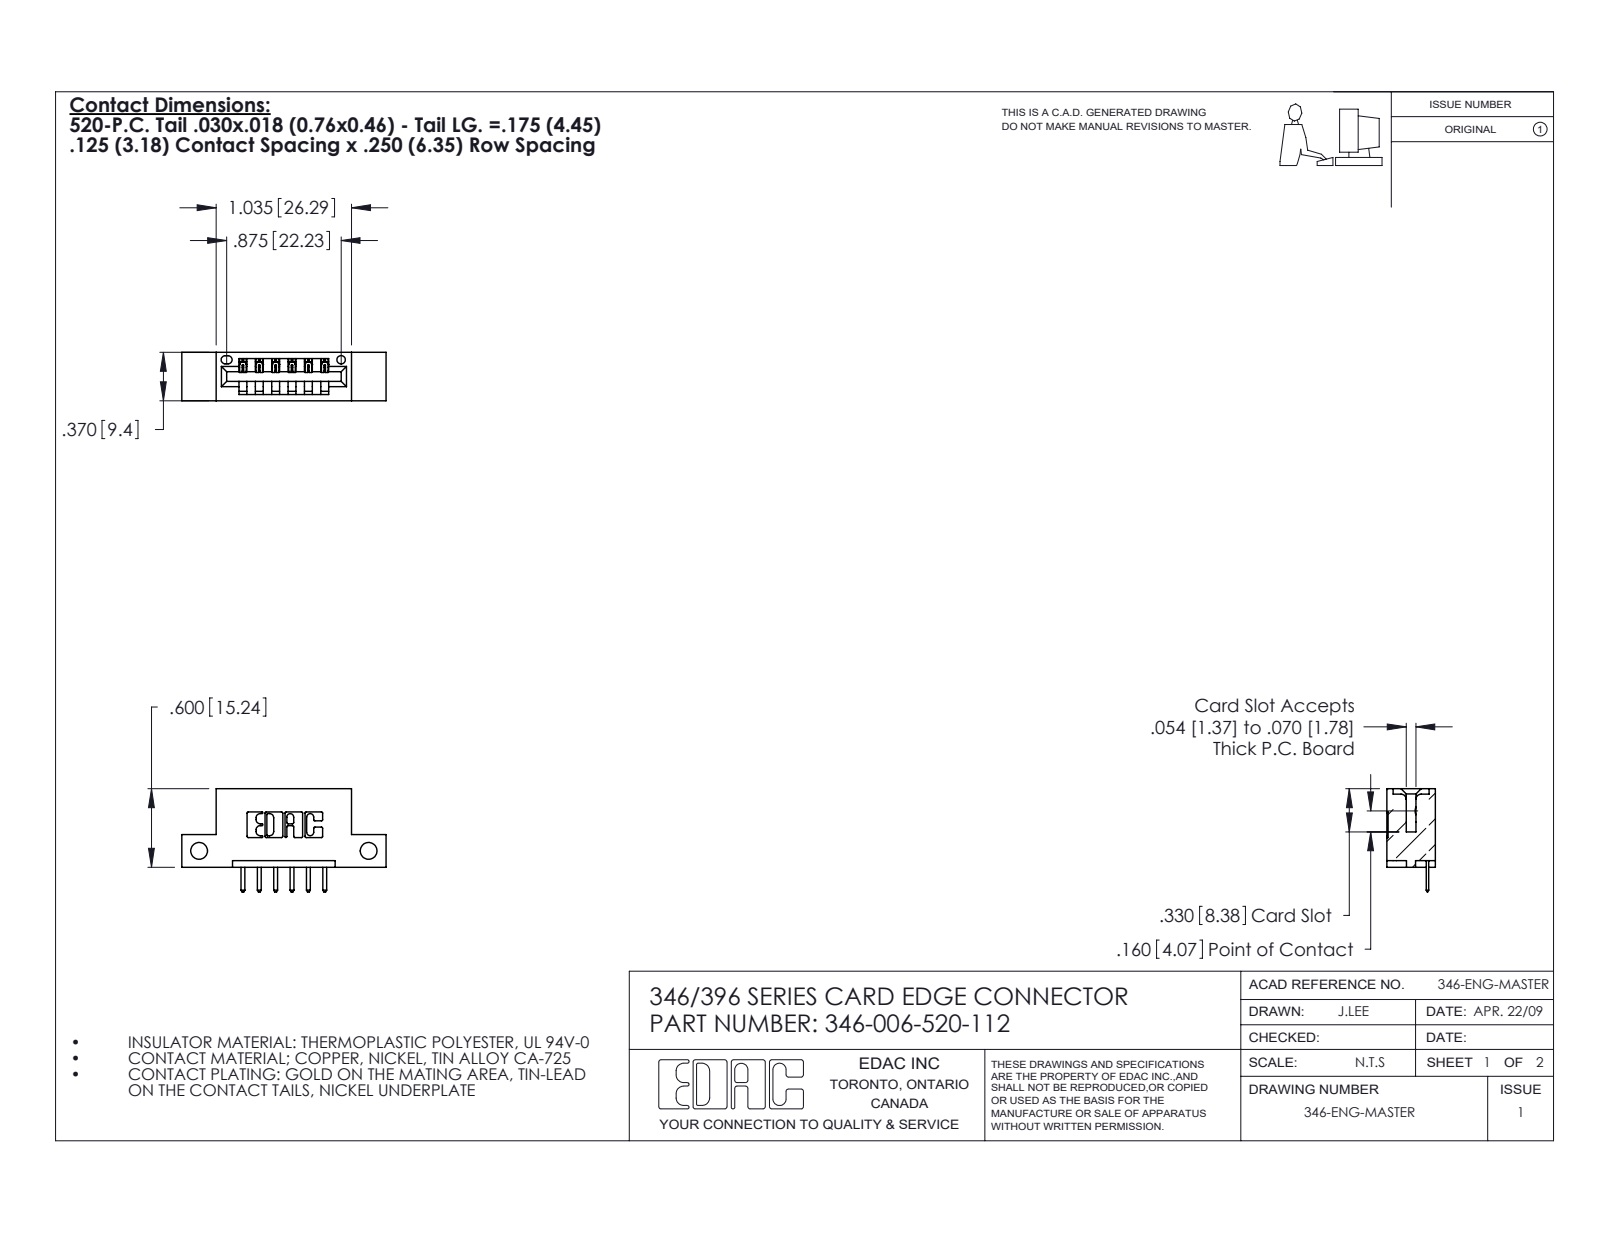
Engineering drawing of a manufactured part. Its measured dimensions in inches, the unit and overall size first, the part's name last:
Units: inches
Overall size (bounding box): 1.56 × 0.788 × 0.37
Round holes (diameter × count): ⌀0.128 ×2, ⌀0.064 ×1
Partial cylindrical surfaces — rounded edges, fillets, slot ends (radius × count): R0.01 ×22, R0.01 ×14, R0.006 ×12, R0.007 ×6, R0.031 ×6, R0.026 ×3, R0.031 ×2, R0.04 ×2
Main face-to-face distances: 0.25, 0.37, 0.048, 0.322, 0.148, 0.222, 0.1, 0.174, 0.125, 0.125
Hole centre spacings: 1.295
Volume: 0.21 in³ · Surface area: 5.748 in²
Bodies: 7 solids, 494 faces (328 planar, 166 cylindrical, 0 other)
Part name (STEP PRODUCT): 346 Part_Flush Mounting Lugs - Side Mount; 346-006-520-112; 345-292-001_345-293-120
STEP written by: SolidWorks 2020 (CONFIG_CONTROL_DESIGN)
